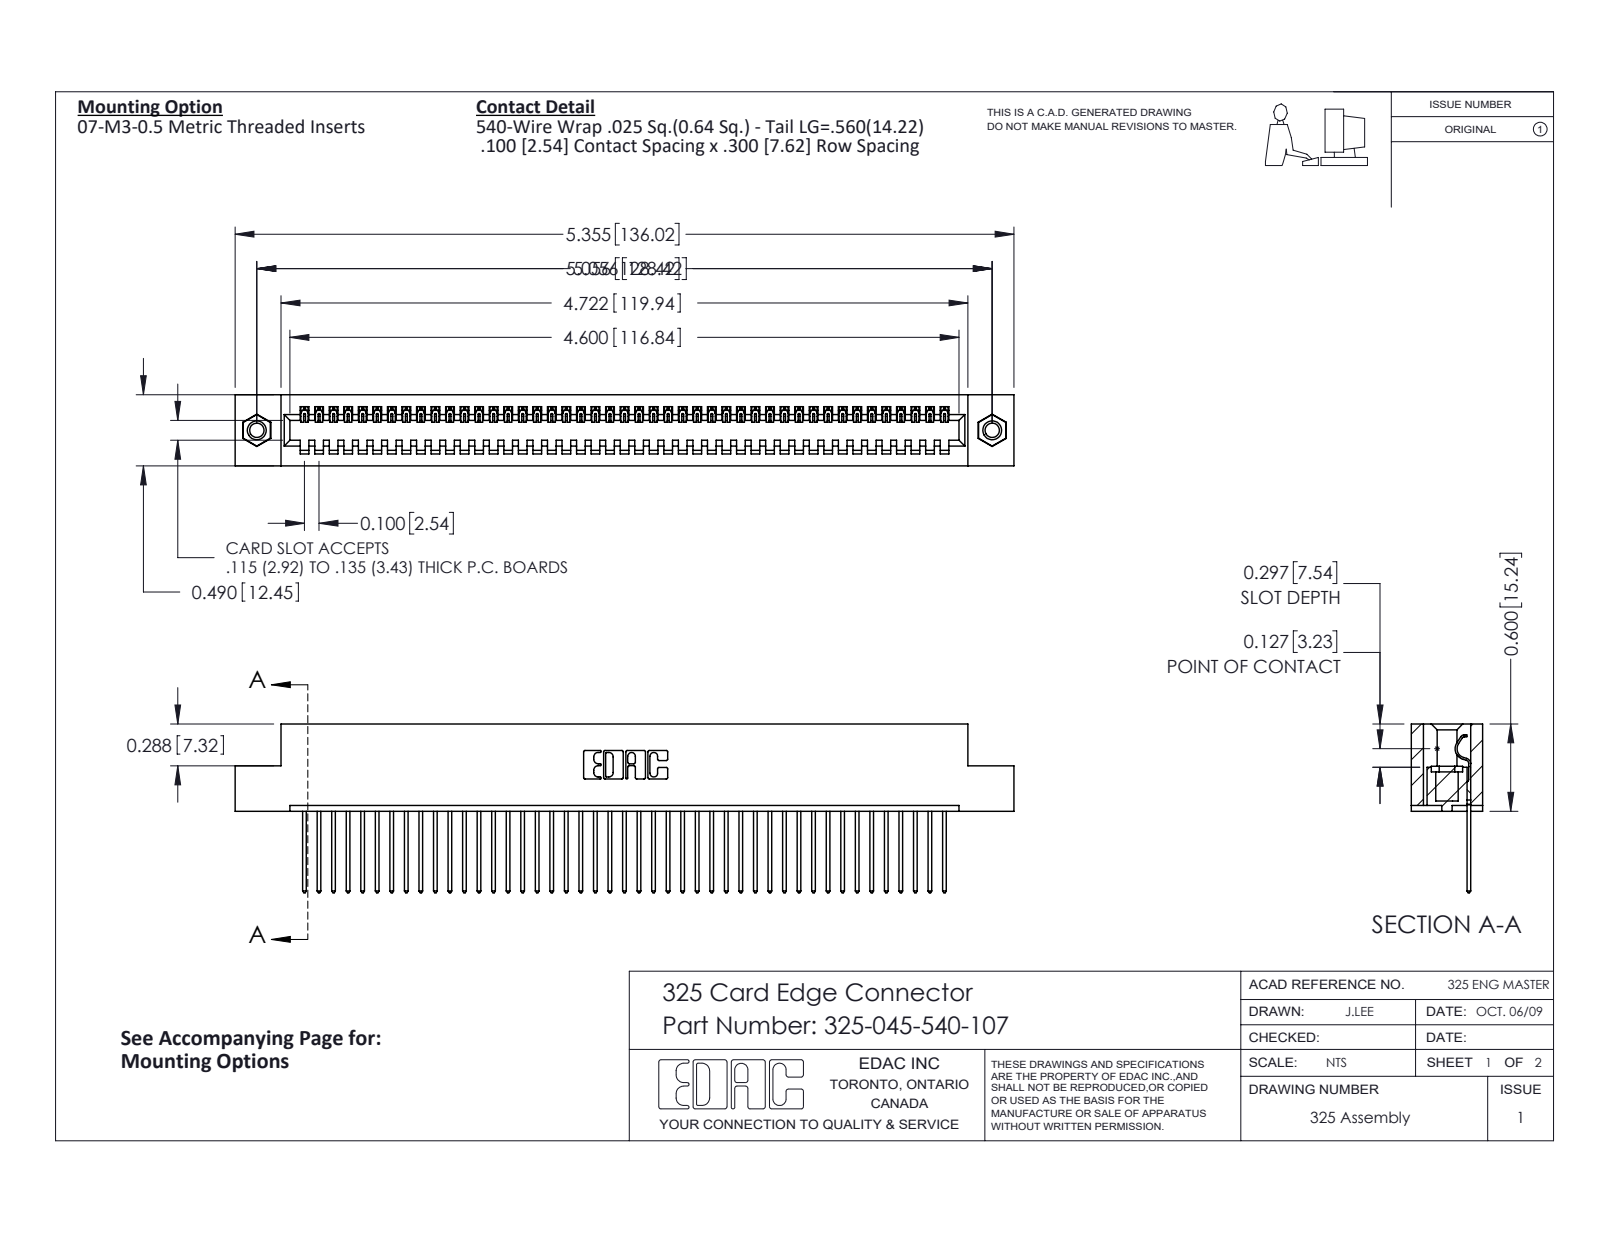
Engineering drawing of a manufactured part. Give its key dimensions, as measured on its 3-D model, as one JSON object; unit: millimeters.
{"part_name": "325-292-001_325-293-140; 345-250-001_345-250-005-103; 325 Part_TI; 325-045-540-107", "step_written_by": "SolidWorks 2016 (CONFIG_CONTROL_DESIGN)", "units": "millimeters", "bodies": {"solids": 48, "faces": 2784, "planar": 1992, "cylindrical": 776, "other": 16}, "overall_size": [136, 29.5, 12.4], "volume_mm3": 17340, "surface_area_mm2": 19470, "round_holes": [[2.5, 2], [3.2, 2], [4.1, 2]], "round_bosses_or_shafts": [[3.9, 2]], "partial_cylinders_radius": [[0.2, 90], [0.3, 90], [0.3, 22], [0.2, 6], [0.8, 6], [0.7, 3], [0.4, 1], [0.6, 1]], "face_to_face_distances": [2.1, 10.3, 12.4, 7.6, 2.7, 9.7, 0.6, 8.3, 14.2, 6.7], "hole_center_spacings": [128.4]}
